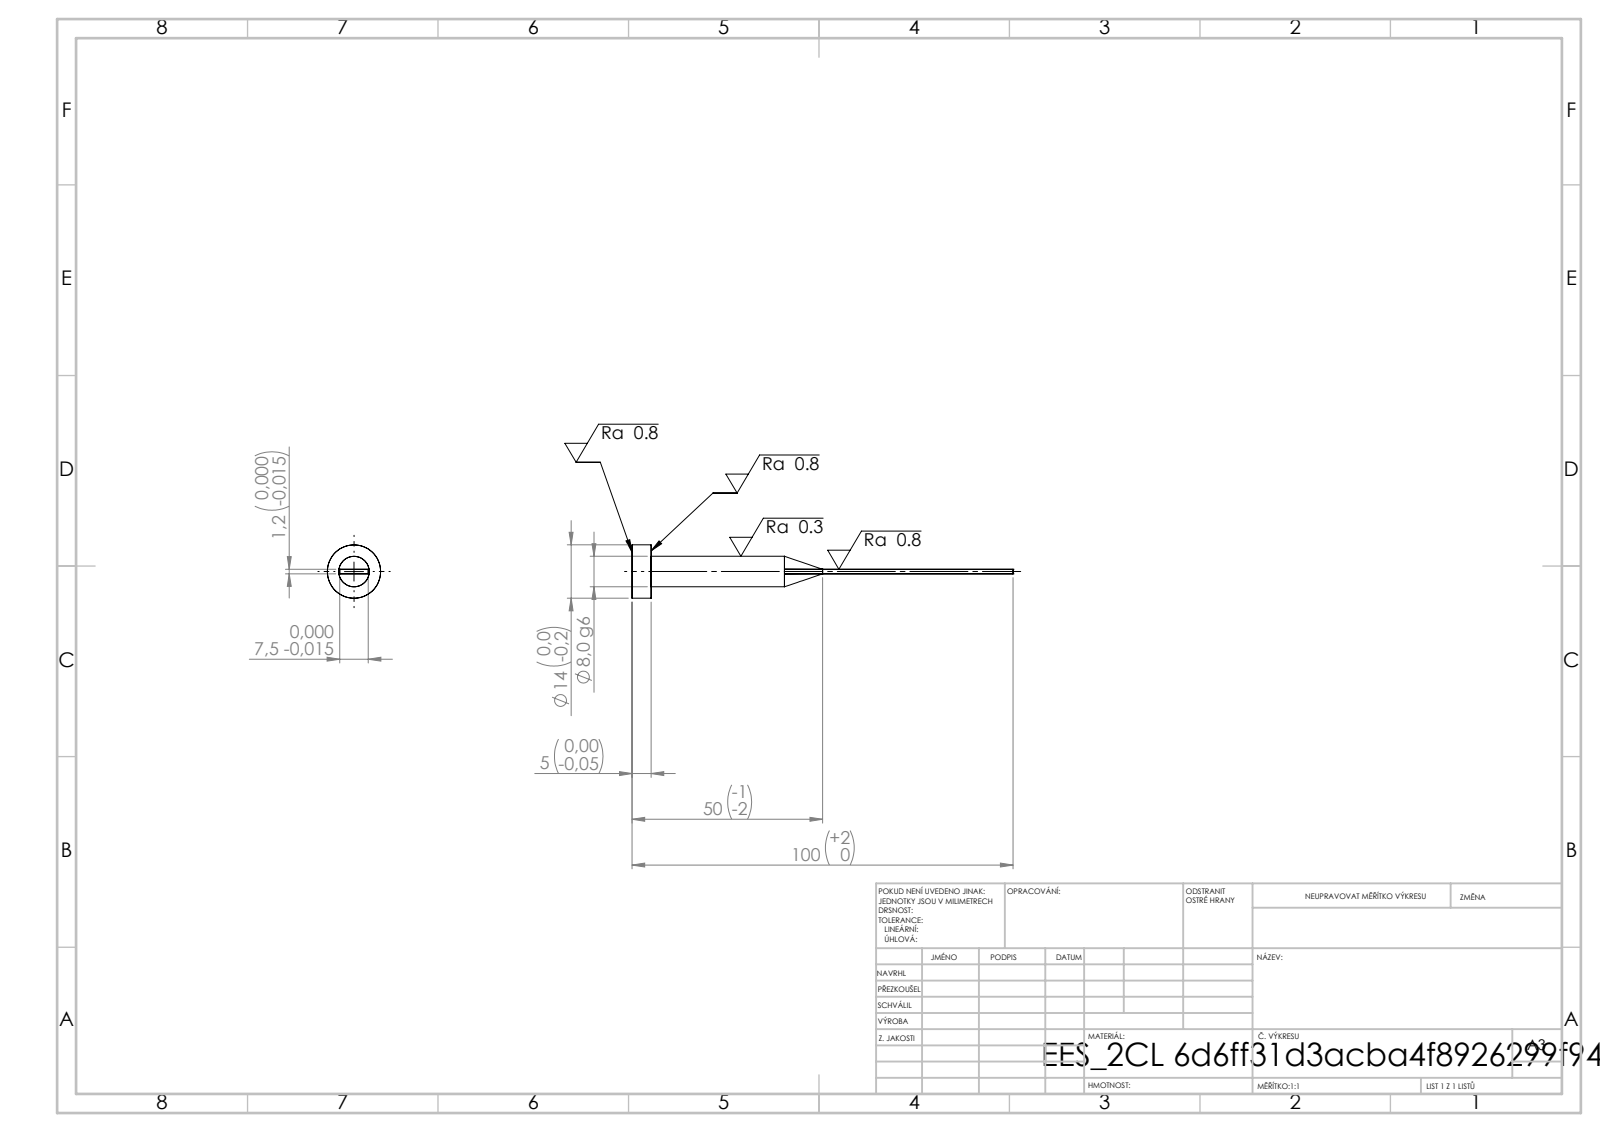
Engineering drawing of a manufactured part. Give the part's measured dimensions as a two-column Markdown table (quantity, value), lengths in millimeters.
| quantity | value |
| --- | --- |
| STEP written by | SolidWorks 2019 (CONFIG_CONTROL_DESIGN) |
| units | millimeters |
| bodies | 1 solid, 15 faces (7 planar, 4 cylindrical, 4 other) |
| overall size | 100 × 14 × 14 |
| volume | 3 258 mm³ |
| surface area | 2 444 mm² |
| round bosses / shafts (diameter × count) | 14 × 1, 8 × 1 |
| main face-to-face distances | 1.2, 5, 7.5, 100, 95 |
